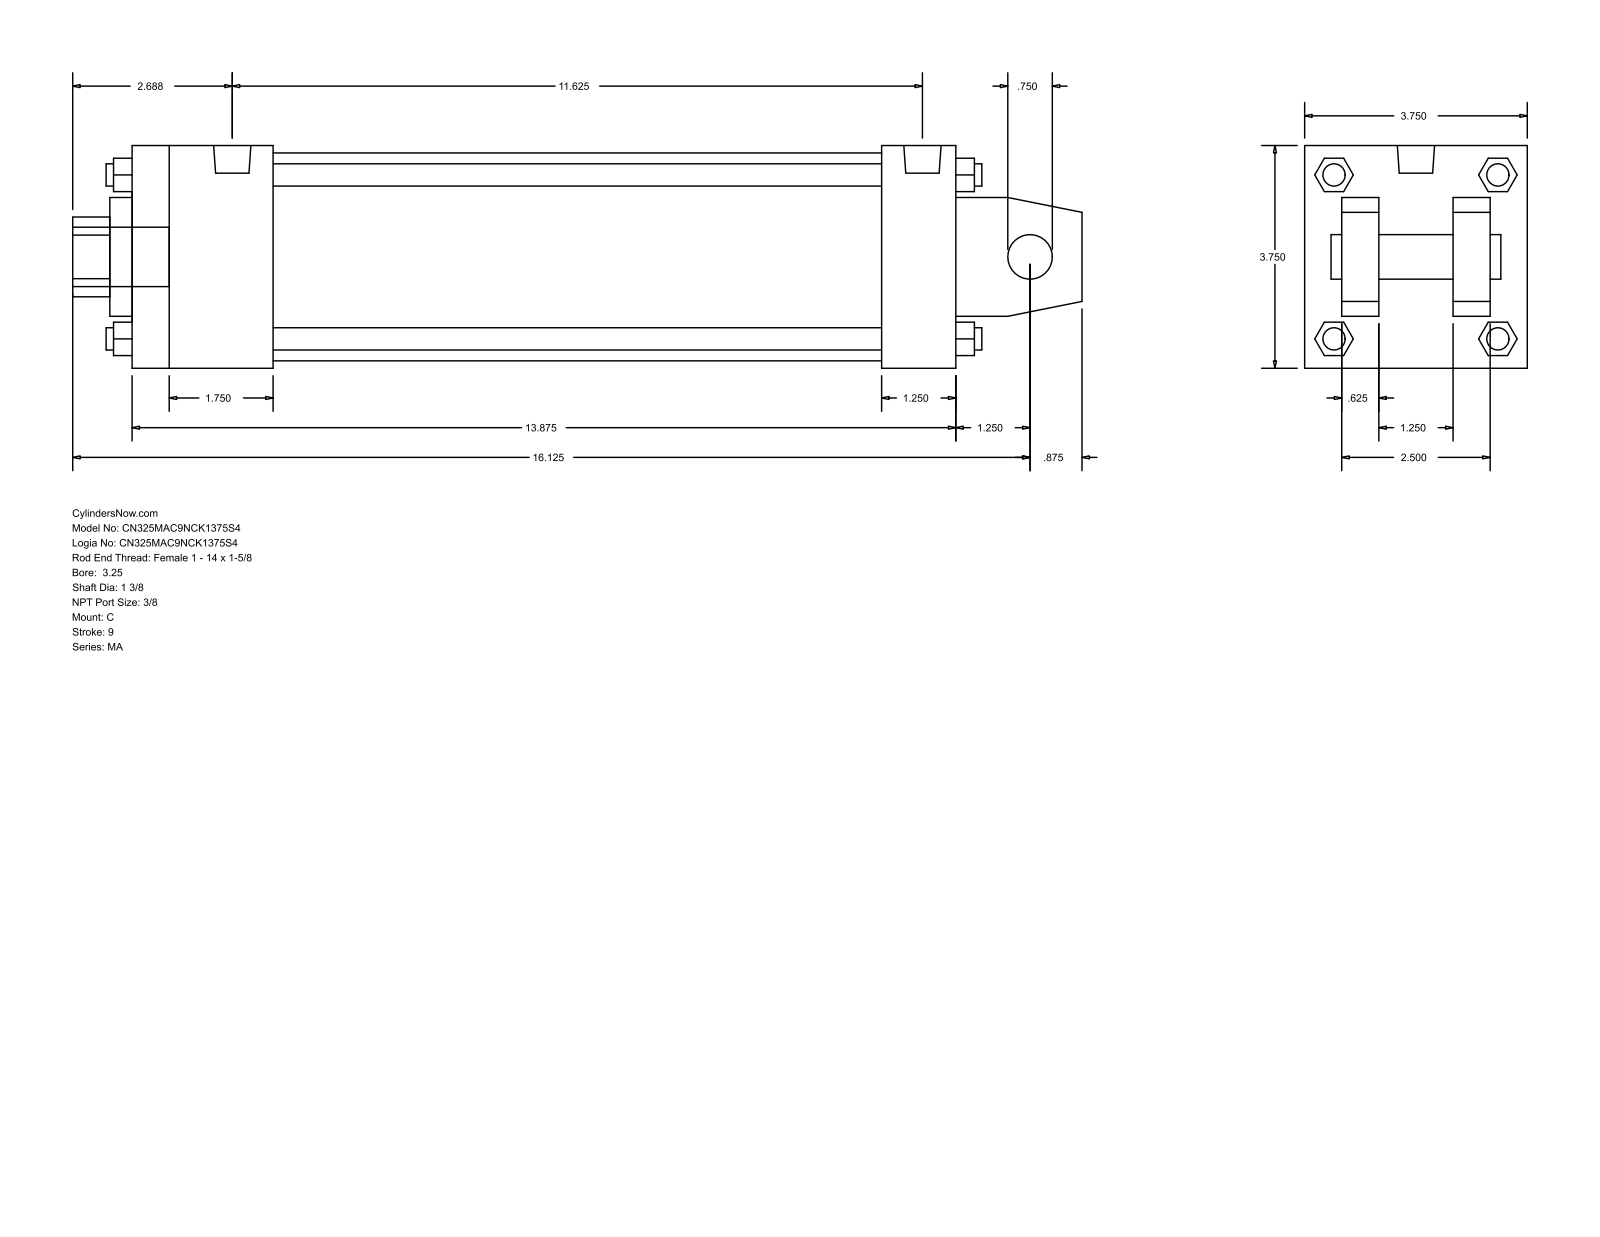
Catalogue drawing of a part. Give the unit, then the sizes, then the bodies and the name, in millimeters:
Units: millimetres
Overall size (bounding box): 431.8 × 95.25 × 95.25
Round holes (diameter × count): ⌀19.05 ×1, ⌀34.92 ×1, ⌀50.8 ×1, ⌀88.9 ×1
Round bosses / shafts (diameter × count): ⌀11.11 ×4, ⌀9.53 ×4, ⌀15.93 ×2, ⌀25.4 ×1
Partial cylindrical surfaces — rounded edges, fillets, slot ends (radius × count): R17.06 ×1
Main face-to-face distances: 95.24, 15.87, 63.5, 352.42, 31.74, 79.37, 47.63, 320.67, 31.75, 60.32
Bodies: 0 solids, 139 faces (108 planar, 31 cylindrical, 0 other)
Part name (STEP PRODUCT): MA_C__0325_1.375
STEP written by: GSSL Pune (CONFIG_CONTROL_DESIGN)
